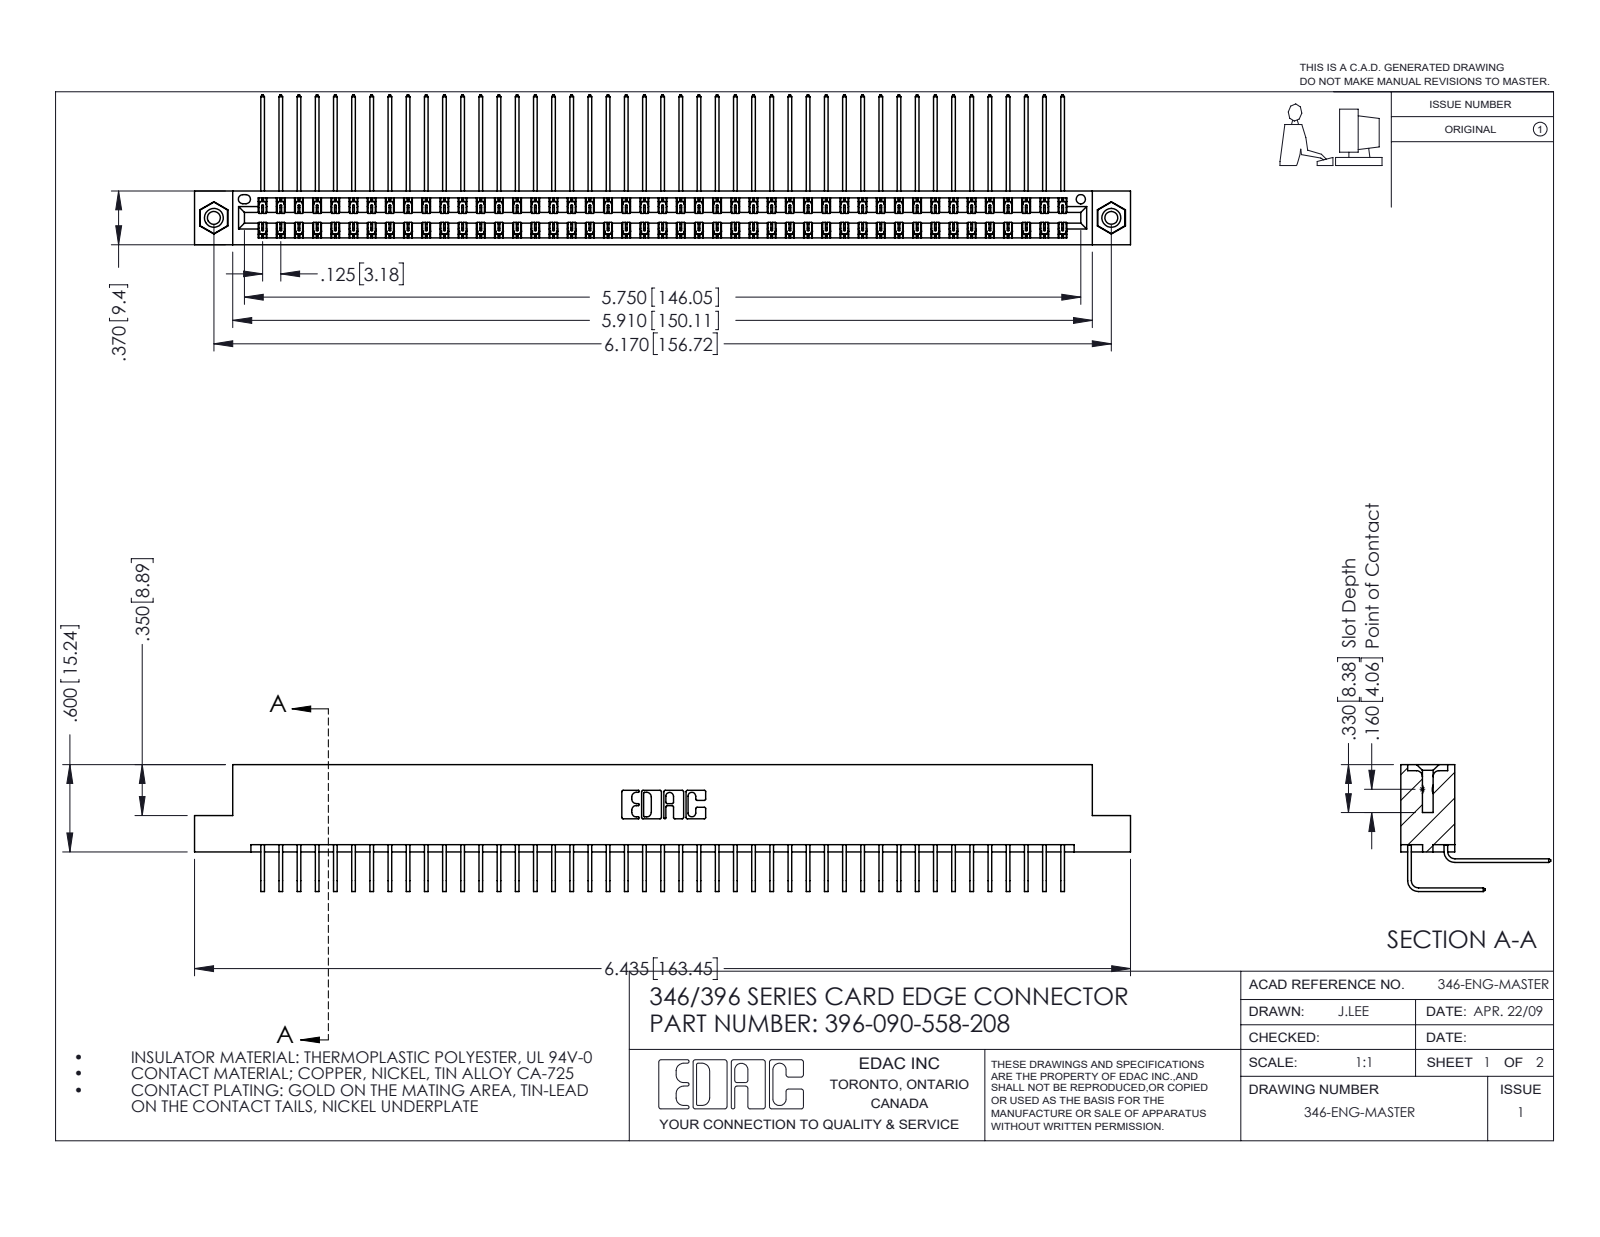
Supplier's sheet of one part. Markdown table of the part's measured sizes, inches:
| quantity | value |
| --- | --- |
| part name | 345-292-001_558 559 Tail - 1; 396-090-558-208; 346 Part_Flush Mounting Lugs - 0.156 Dia-TI; 345-292-001_558 Tail - 2 (+1 more) |
| STEP written by | SolidWorks 2016 (CONFIG_CONTROL_DESIGN) |
| units | inches |
| bodies | 93 solids, 5042 faces (3438 planar, 1588 cylindrical, 16 other) |
| overall size | 6.435 × 1.03 × 0.873 |
| volume | 1.005 in³ |
| surface area | 39.06 in² |
| round holes (diameter × count) | 0.089 × 2, 0.125 × 2, 0.156 × 2, 0.064 × 1 |
| round bosses / shafts (diameter × count) | 0.155 × 2 |
| partial cylindrical surfaces (radius × count) | 0.006 × 135, 0.01 × 22, 0.007 × 6, 0.031 × 6, 0.026 × 3, 0.014 × 2, 0.022 × 2, 0.024 × 2 |
| main face-to-face distances | 0.048, 0.322, 0.025, 0.37, 0.072, 0.25, 0.298, 0.275, 0.148, 0.222 |
| hole center spacings | 0.246, 5.961, 6.17 |
